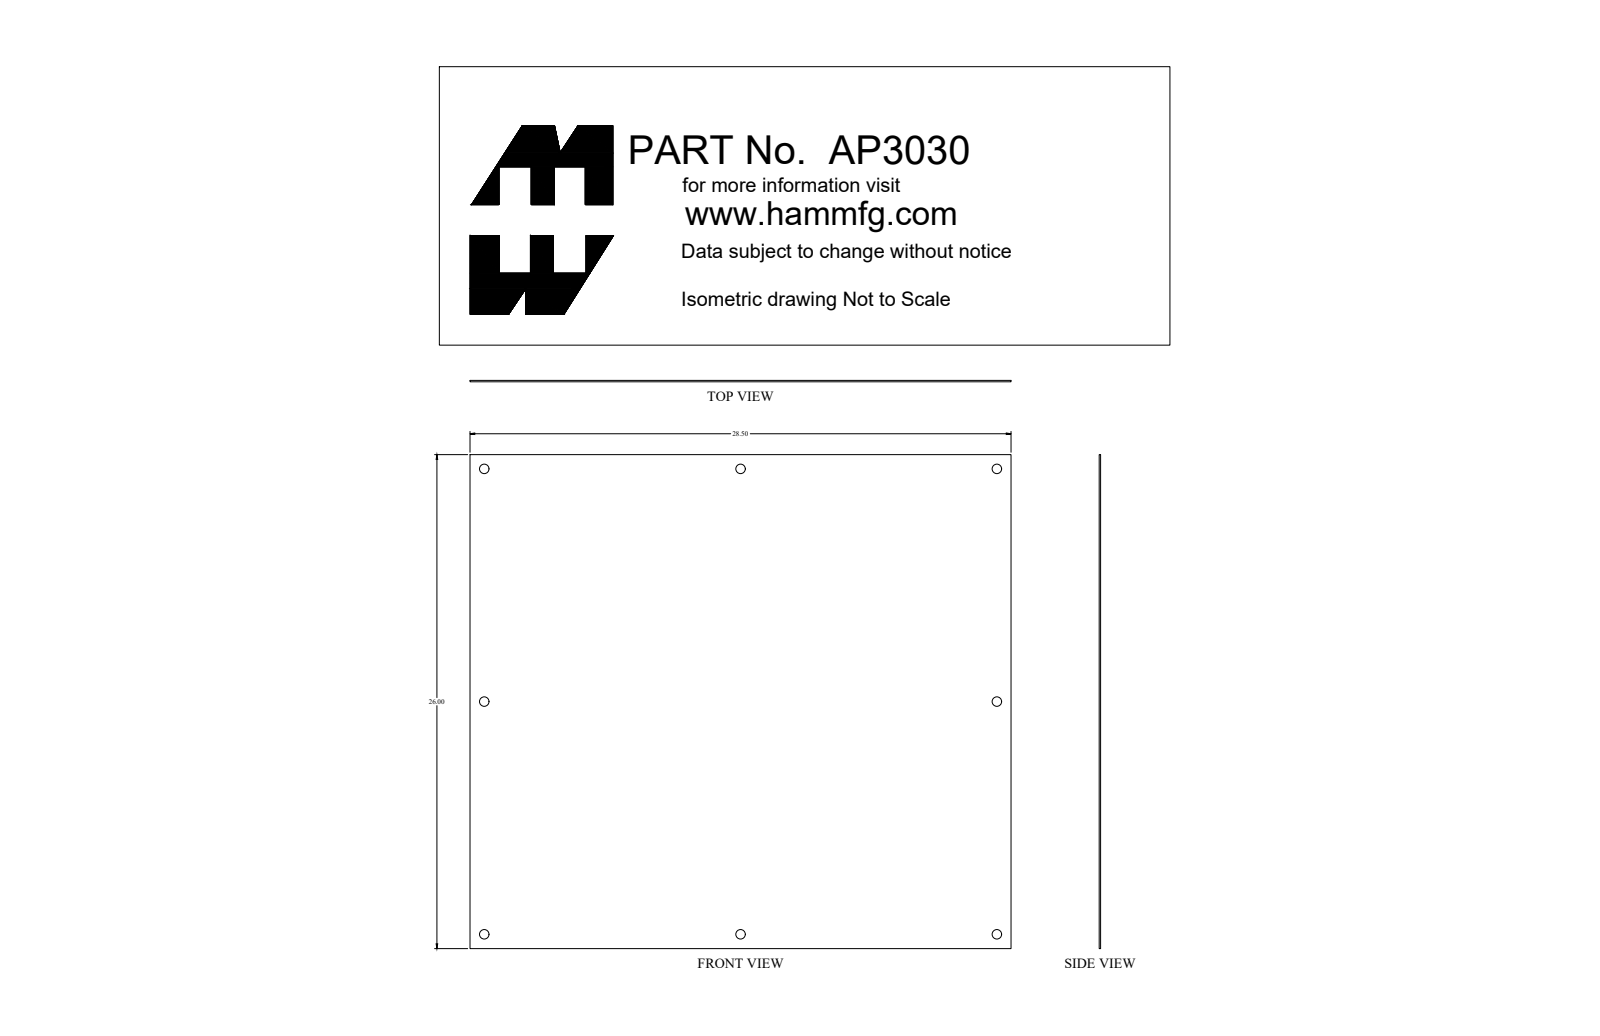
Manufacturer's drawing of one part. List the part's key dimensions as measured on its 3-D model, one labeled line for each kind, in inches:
Part name (STEP PRODUCT): AP3030_Default
STEP written by: SolidWorks 2019 (CONFIG_CONTROL_DESIGN)
Units: inches
Bodies: 1 solid, 22 faces (6 planar, 16 cylindrical, 0 other)
Overall size (bounding box): 28.5 × 26 × 0.072
Volume: 53.24 in³ · Surface area: 1 488 in²
Round holes (diameter × count): ⌀0.5 ×8
Main face-to-face distances: 0.072, 26, 28.5
Hole centre spacings: 12.25, 13.5, 18.23, 27.973, 29.649, 24.5, 27, 36.459
